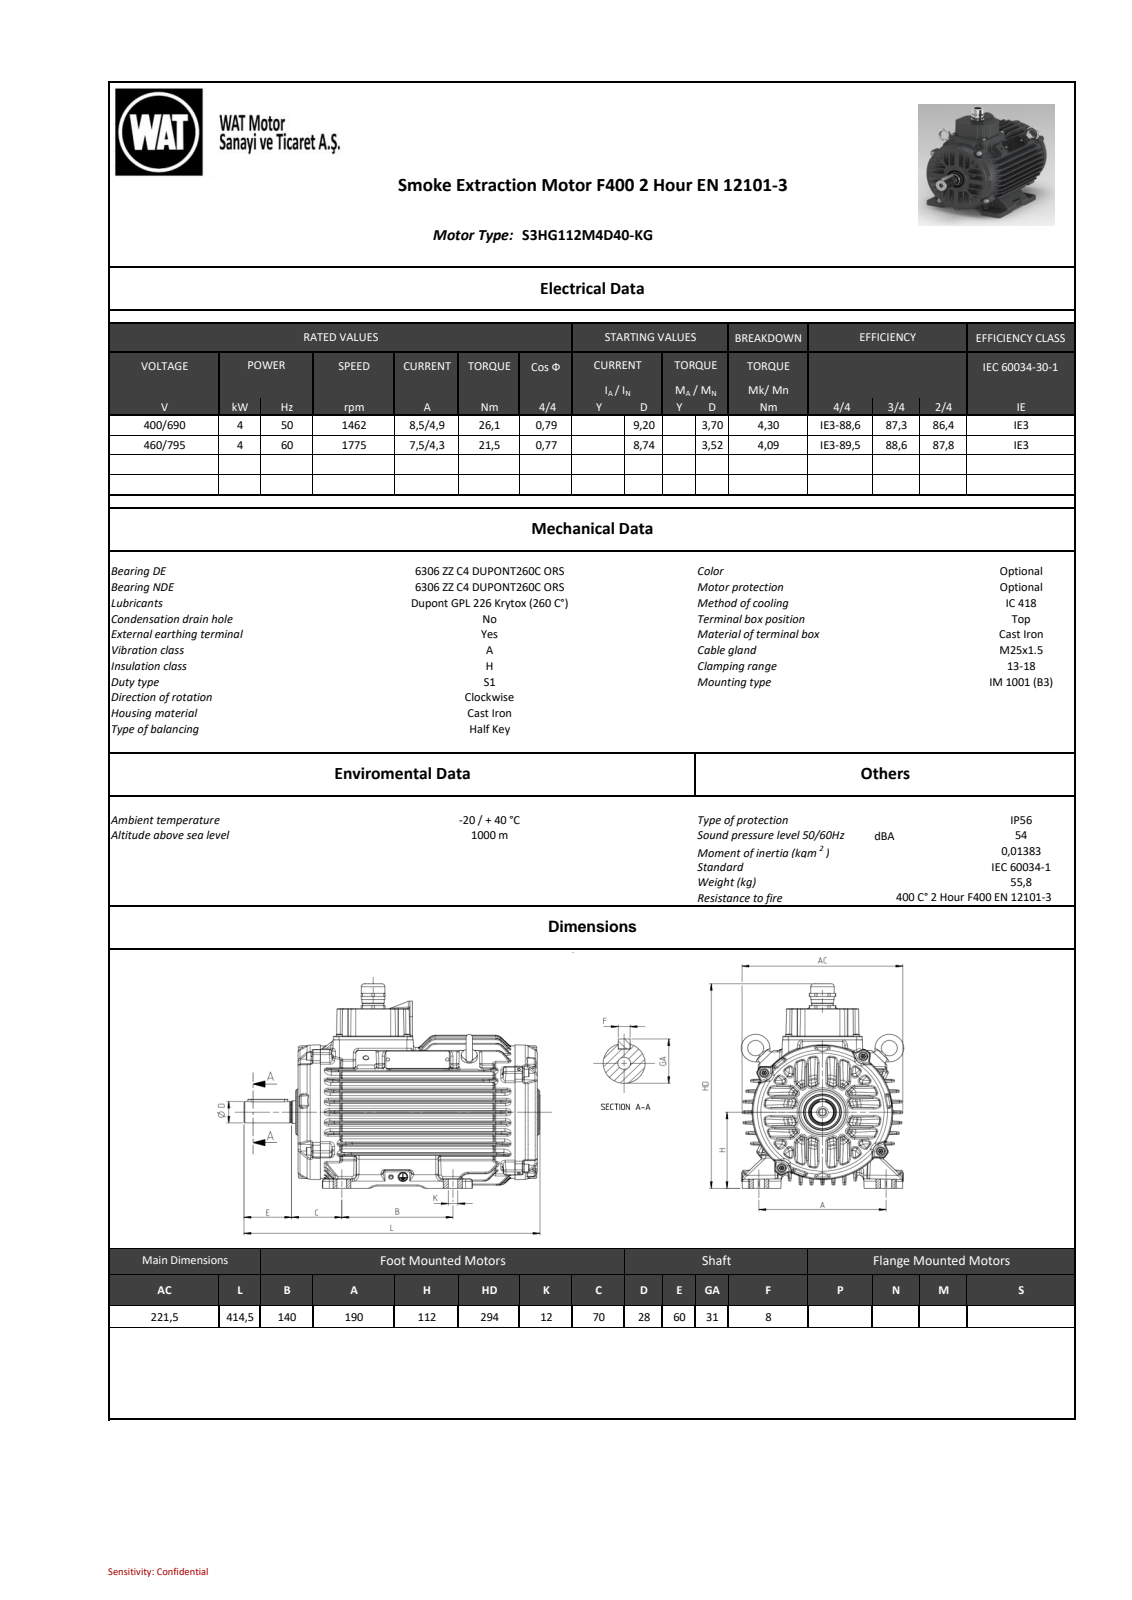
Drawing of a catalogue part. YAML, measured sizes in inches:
part_name: "26032C0836B7xipc"
step_written_by: "SIEMENS PLM Software NX 11.0 (AUTOMOTIVE_DESIGN)"
units: inches
bodies: {solids: 0, faces: 5916, planar: 830, cylindrical: 1334, other: 3752}
overall_size: [16.319, 11.563, 9.803]
round_holes:
  - {diameter: 0.197, count: 9}
  - {diameter: 0.138, count: 4}
  - {diameter: 0.098, count: 2}
  - {diameter: 0.268, count: 2}
  - {diameter: 0.335, count: 1}
  - {diameter: 0.413, count: 1}
  - {diameter: 0.709, count: 1}
  - {diameter: 1.299, count: 1}
  - {diameter: 1.693, count: 1}
round_bosses_or_shafts:
  - {diameter: 0.492, count: 8}
  - {diameter: 0.394, count: 4}
  - {diameter: 0.385, count: 4}
  - {diameter: 0.315, count: 4}
  - {diameter: 0.787, count: 2}
  - {diameter: 7.559, count: 1}
  - {diameter: 1.85, count: 1}
  - {diameter: 1.181, count: 1}
partial_cylinders:
  - {radius: 0.157, count: 285}
  - {radius: 0.118, count: 188}
  - {radius: 0.059, count: 98}
  - {radius: 0.079, count: 62}
  - {radius: 0.197, count: 57}
  - {radius: 0.071, count: 48}
  - {radius: 0.039, count: 36}
  - {radius: 0.01, count: 26}
face_to_face_distances: [0.516, 1.573, 1.035, 0.519, 3.565, 1.557, 1.041, 0.522, 3.046, 2.53]
hole_center_spacings: [3.819, 5.401, 1.326, 4.381, 6.257, 7.522, 7.638, 1.083]
